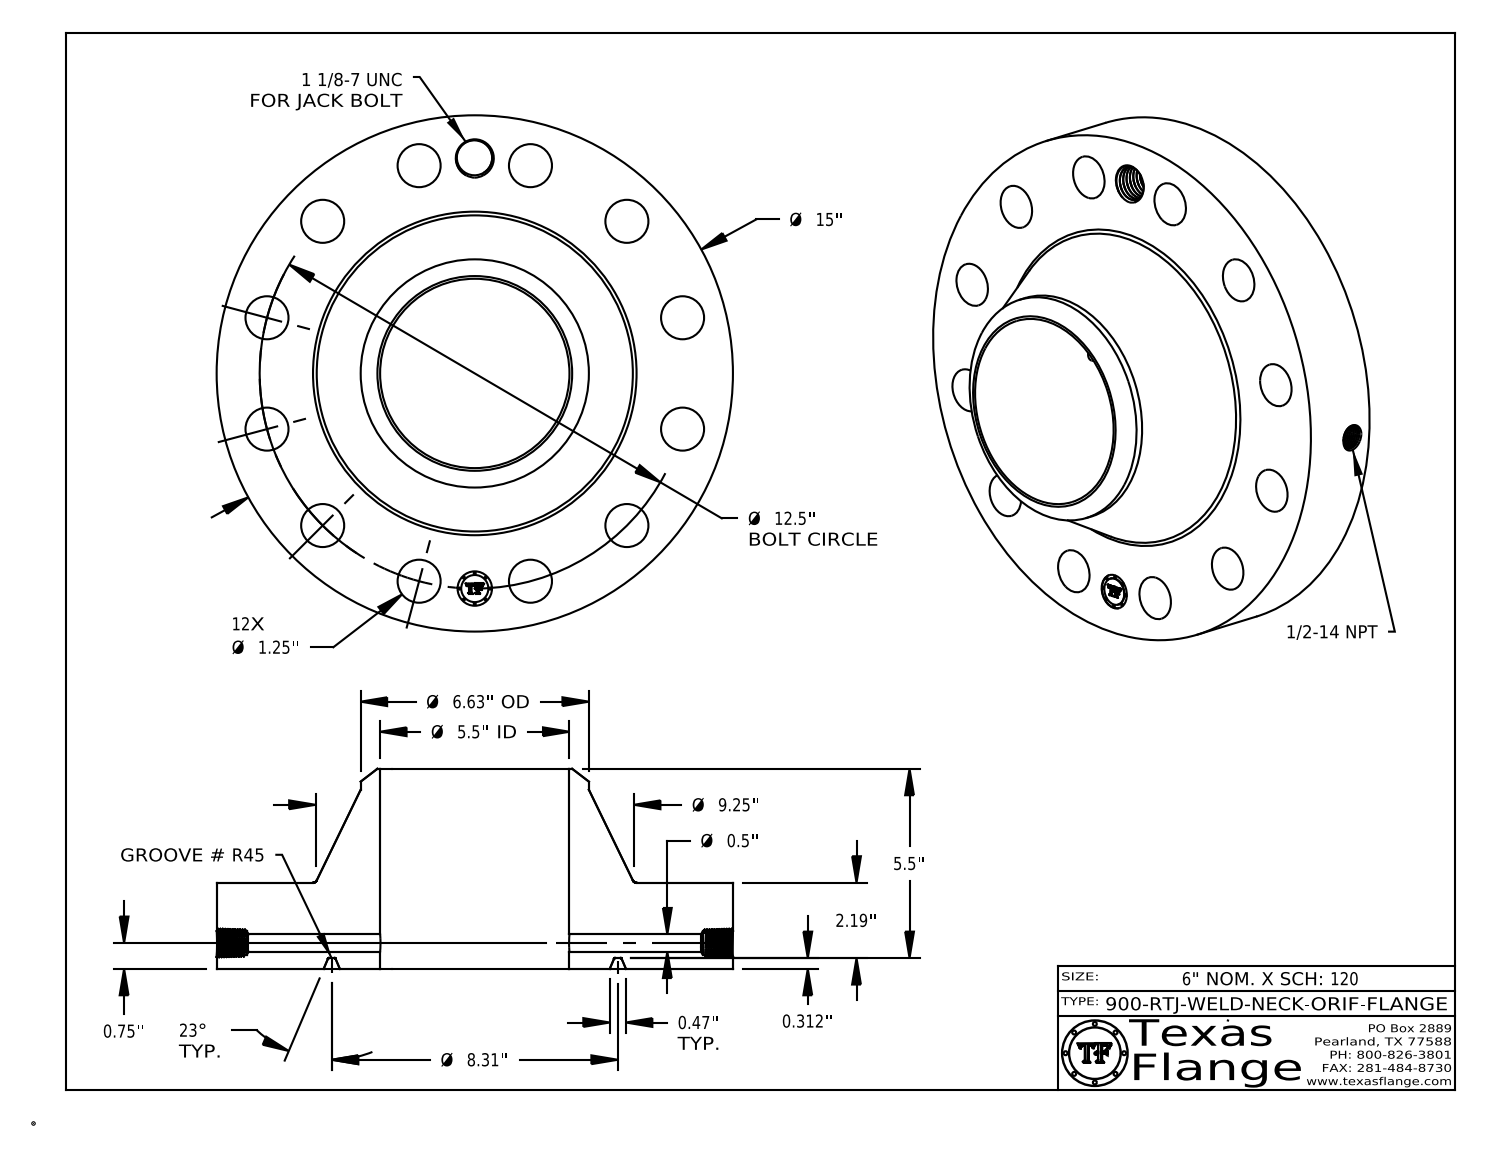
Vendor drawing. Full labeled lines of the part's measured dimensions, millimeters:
Part name (STEP PRODUCT): 900-RTJ-WELD-NECK
STEP written by: CATIA V5 STEP AP214 (AUTOMOTIVE_DESIGN)
Units: millimetres
Bodies: 1 solid, 801 faces (370 planar, 105 cylindrical, 326 other)
Overall size (bounding box): 381 × 381 × 147.6
Volume: 6 788 000 mm³ · Surface area: 452 000 mm²
Round holes (diameter × count): ⌀31.8 ×12, ⌀12.7 ×1, ⌀17.1 ×1, ⌀25 ×1, ⌀25.4 ×1, ⌀139.7 ×1
Round bosses / shafts (diameter × count): ⌀1.5 ×8, ⌀381 ×1, ⌀168.4 ×1, ⌀20 ×1
Main face-to-face distances: 63.6, 7.9, 55.6, 147.6, 139.7, 84.1, 63.2, 55.2, 0.4, 84.5
Hole centre spacings: 158.8, 306.7, 82.2, 224.5, 275, 317.5, 41.4, 82.2
